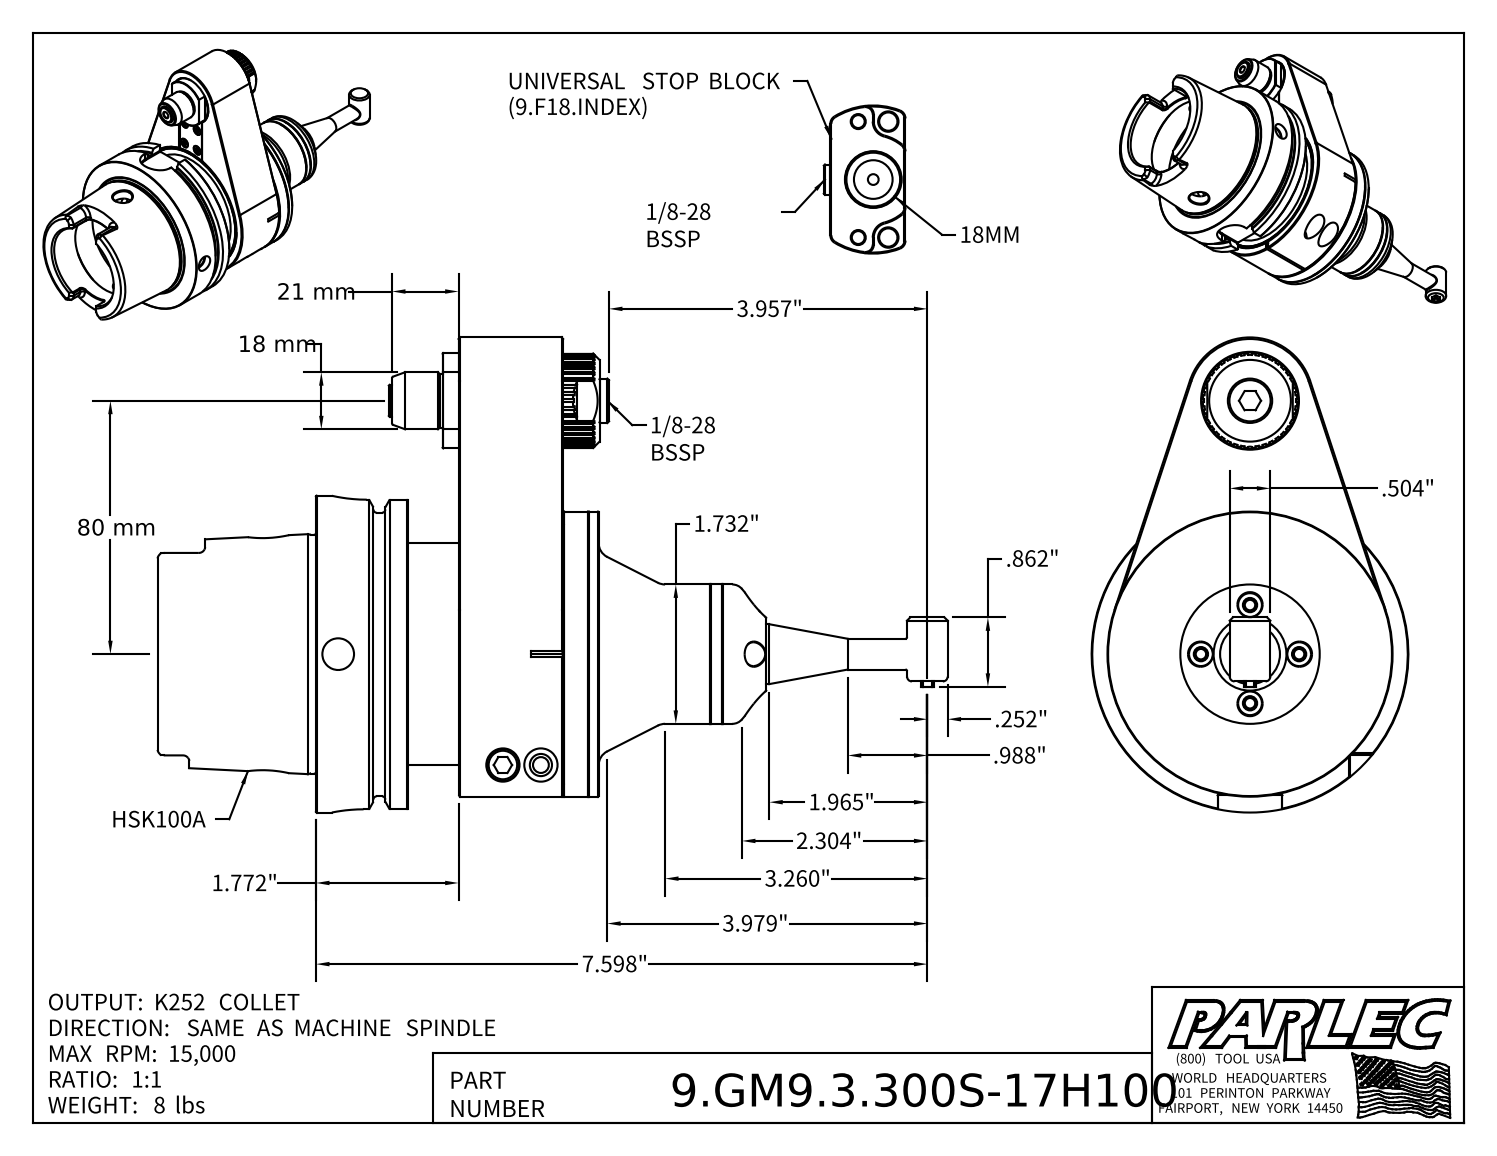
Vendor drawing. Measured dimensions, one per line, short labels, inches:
name: 9.GM9.3.300S-17H100
written by: Autodesk Inventor 2022 (AUTOMOTIVE_DESIGN)
unit: in
bodies: 2 solids, 916 faces (445 planar, 218 cylindrical, 253 other)
size: 11.343 × 5.906 × 3.937
volume: 42.86 in³; area: 216.8 in²
holes: 3× ⌀0.165, 3× ⌀0.197, 2× ⌀0.157, 2× ⌀0.276, 2× ⌀0.335, 2× ⌀0.413, 2× ⌀0.472, 2× ⌀0.512, 1× ⌀0.13, 1× ⌀0.217, 1× ⌀0.256, 1× ⌀0.362
bosses: 6× ⌀0.276, 4× ⌀0.394, 4× ⌀0.224, 4× ⌀0.157, 2× ⌀0.669, 2× ⌀0.236, 1× ⌀3.937, 1× ⌀3.622
rounds: 8× R0.079, 8× R0.089, 8× R0.148, 3× R0.394, 2× R0.033, 2× R0.085, 1× R0.059, 1× R0.118
face distances: 0.965, 1.929, 0.63, 1.142, 1.772, 1.299, 3.071, 0.748, 0.118, 1.89
hole spacings: 0.61, 0.644, 2.572, 4.044, 0.177, 0.472, 0.512, 1.13
